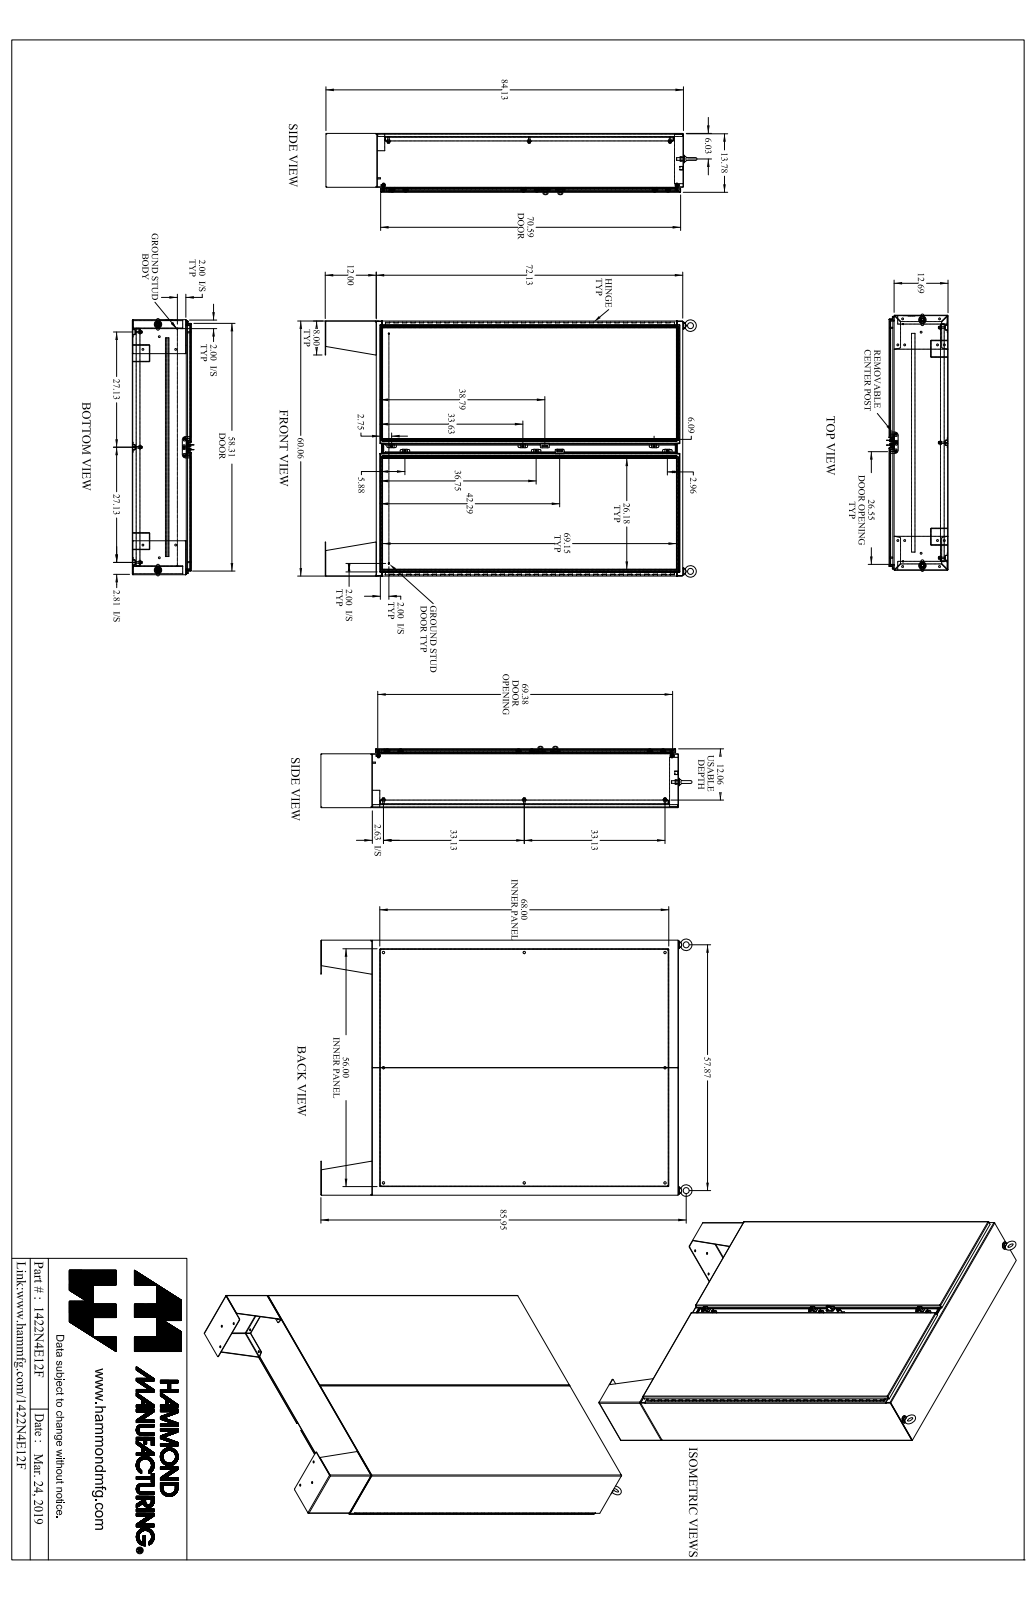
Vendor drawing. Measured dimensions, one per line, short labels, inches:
name: 1422N4E12F_Default
written by: SolidWorks 2019 (CONFIG_CONTROL_DESIGN)
unit: in
bodies: 109 solids, 3636 faces (1846 planar, 1578 cylindrical, 212 other)
size: 87.778 × 61.121 × 14.468
volume: 2 102 in³; area: 39 687 in²
holes: 24× ⌀0.304, 14× ⌀0.437, 8× ⌀0.307, 8× ⌀0.563, 6× ⌀0.213, 6× ⌀0.265, 6× ⌀0.445, 3× ⌀0.201, 3× ⌀0.25, 3× ⌀0.313, 3× ⌀0.375, 3× ⌀0.375
bosses: 8× ⌀1, 8× ⌀0.65, 8× ⌀0.375, 8× ⌀0.33, 6× ⌀0.5, 6× ⌀0.39, 6× ⌀0.244, 4× ⌀0.281
rounds: 67× R0.048, 67× R0.143, 34× R0.25, 18× R0.06, 12× R0.116, 12× R0.141, 12× R0.185, 9× R0.187
face distances: 0.095, 0.125, 13.78, 13.655, 11.968, 13.75, 13.875, 0.125, 12.063, 1.687
hole spacings: 6, 58.513, 12, 59.429, 18, 60.924, 24, 62.959
